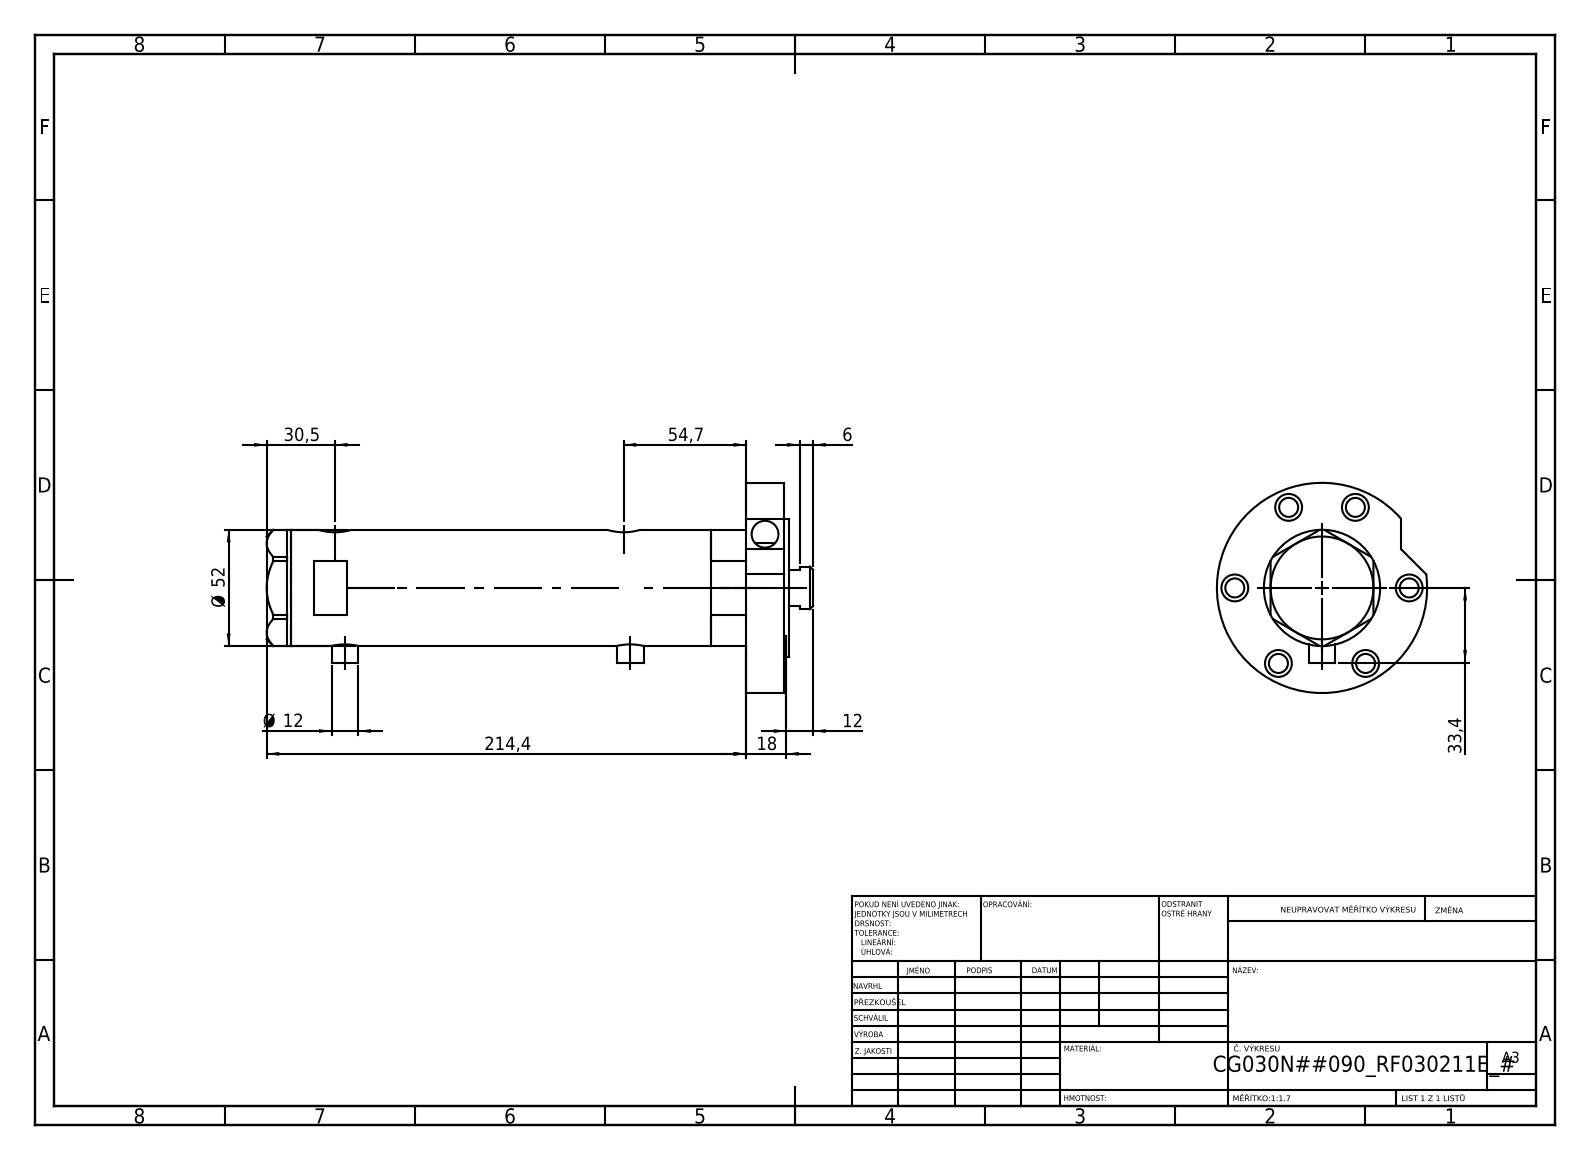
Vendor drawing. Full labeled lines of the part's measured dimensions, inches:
Part name (STEP PRODUCT): V270CG_MIDDLE; V270CG_VC; V270CG_BACK; V270CG_FRONT (+1 more)
STEP written by: SolidWorks 2019 (CONFIG_CONTROL_DESIGN)
Units: inches
Bodies: 5 solids, 178 faces (76 planar, 82 cylindrical, 20 other)
Overall size (bounding box): 9.622 × 3.701 × 3.701
Volume: 31.77 in³ · Surface area: 186.2 in²
Round holes (diameter × count): ⌀0.472 ×7, ⌀0.335 ×6, ⌀0.383 ×2, ⌀0.492 ×2, ⌀0.591 ×2, ⌀0.256 ×1, ⌀0.787 ×1, ⌀0.846 ×1, ⌀1.181 ×1, ⌀1.299 ×1, ⌀1.575 ×1, ⌀1.732 ×1
Round bosses / shafts (diameter × count): ⌀0.472 ×2, ⌀3.701 ×1, ⌀2.441 ×1, ⌀2.047 ×1, ⌀1.496 ×1, ⌀0.748 ×1
Main face-to-face distances: 0.669, 8.008, 8.677, 0.079, 8.756, 5.965, 2.043, 2.713, 0.433, 9.189
Hole centre spacings: 1.535, 1.706, 2.553, 2.659, 2.754, 3.064, 0.114, 0.177
